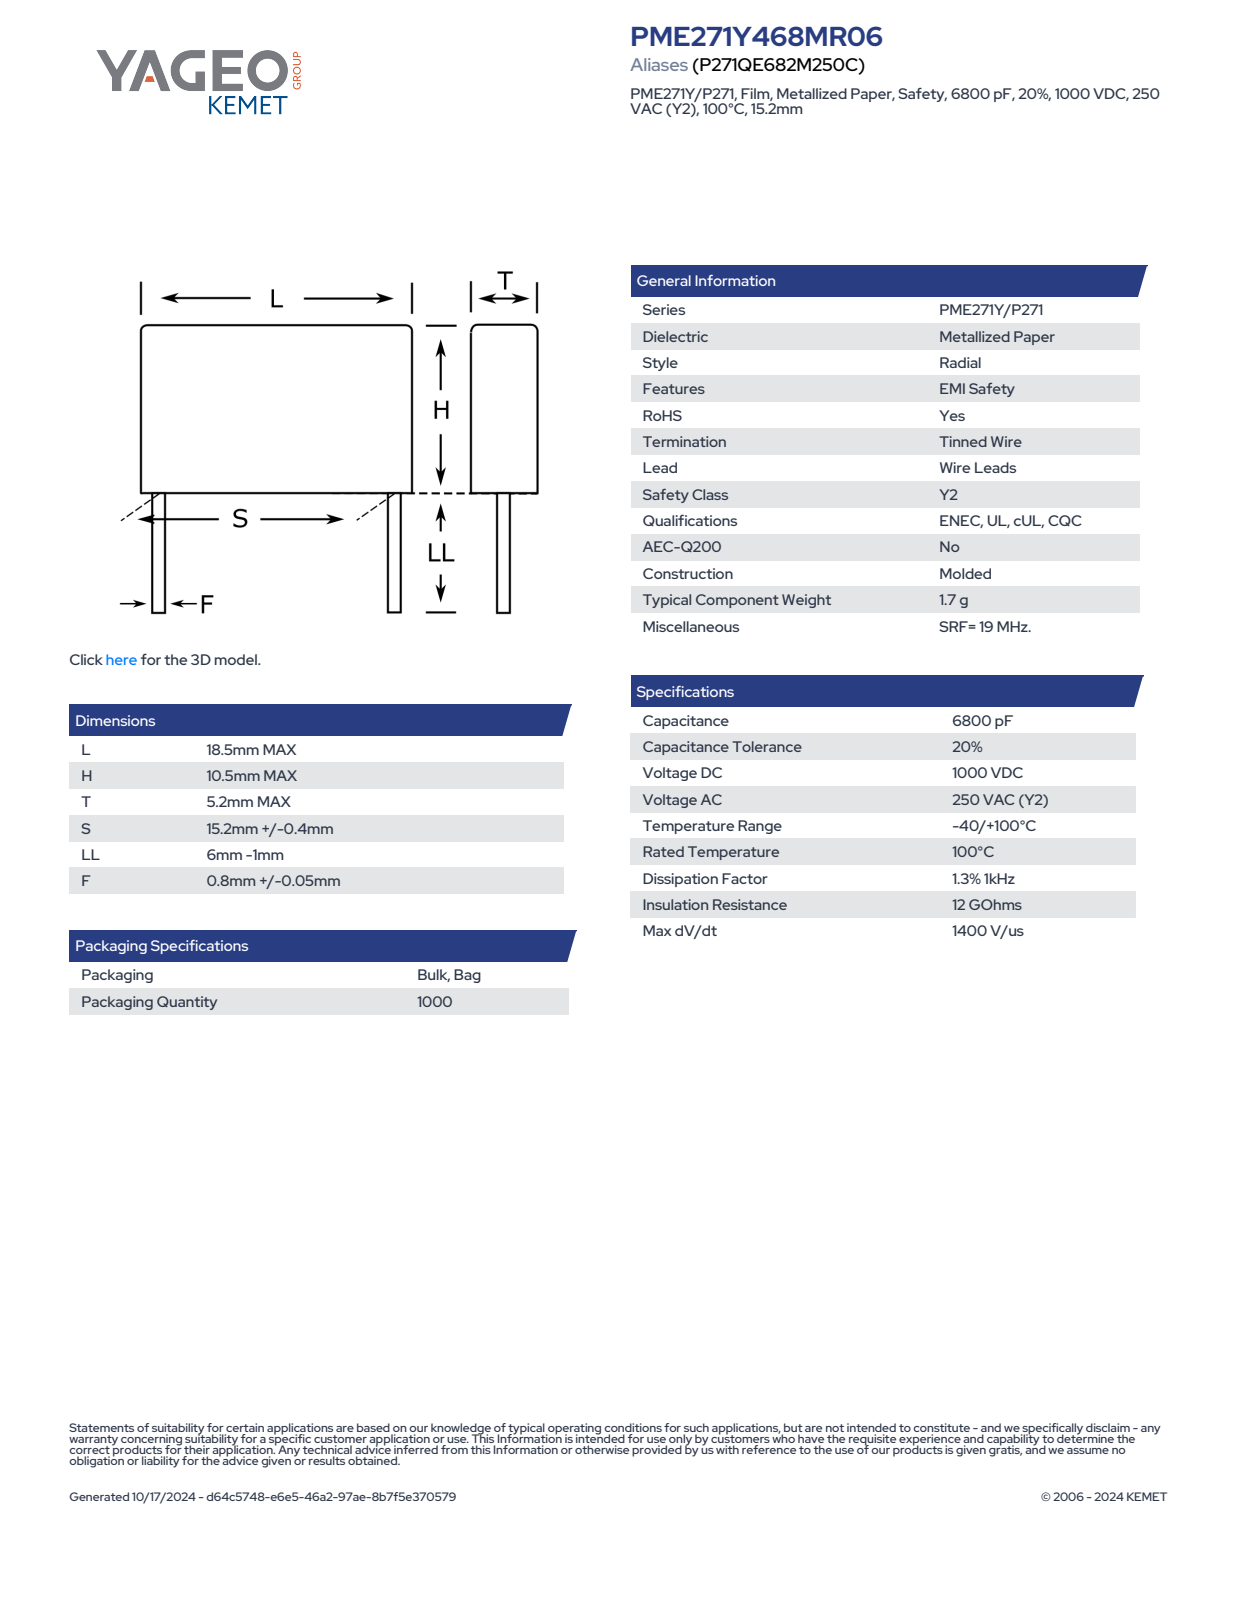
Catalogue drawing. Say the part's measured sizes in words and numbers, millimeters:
The part is named "CFR_MOLDED_18.5X10.5X5.2_L18.5H10.5T5.2S15.2LL5F0.85". Its 3-D file was written by "SolidWorks 2014 (AUTOMOTIVE_DESIGN)". It is 4 solids with 73 faces: 65 planar, 8 cylindrical and 0 other. Overall it measures 18.5 by 15.5 by 5.21 millimeters. Its volume is 1 013 cubic millimeters and its surface area 723 square millimeters. Round bosses or shafts: 2 of diameter 0.85. Partial cylindrical surfaces (rounded edges, fillets, slot ends): 4 of radius 0.5. The main face-to-face distances are 5.2, 10.5, 18.5, 5, 15.5, 11.06, 6.06, 4.44, 9.4, 4.4.
